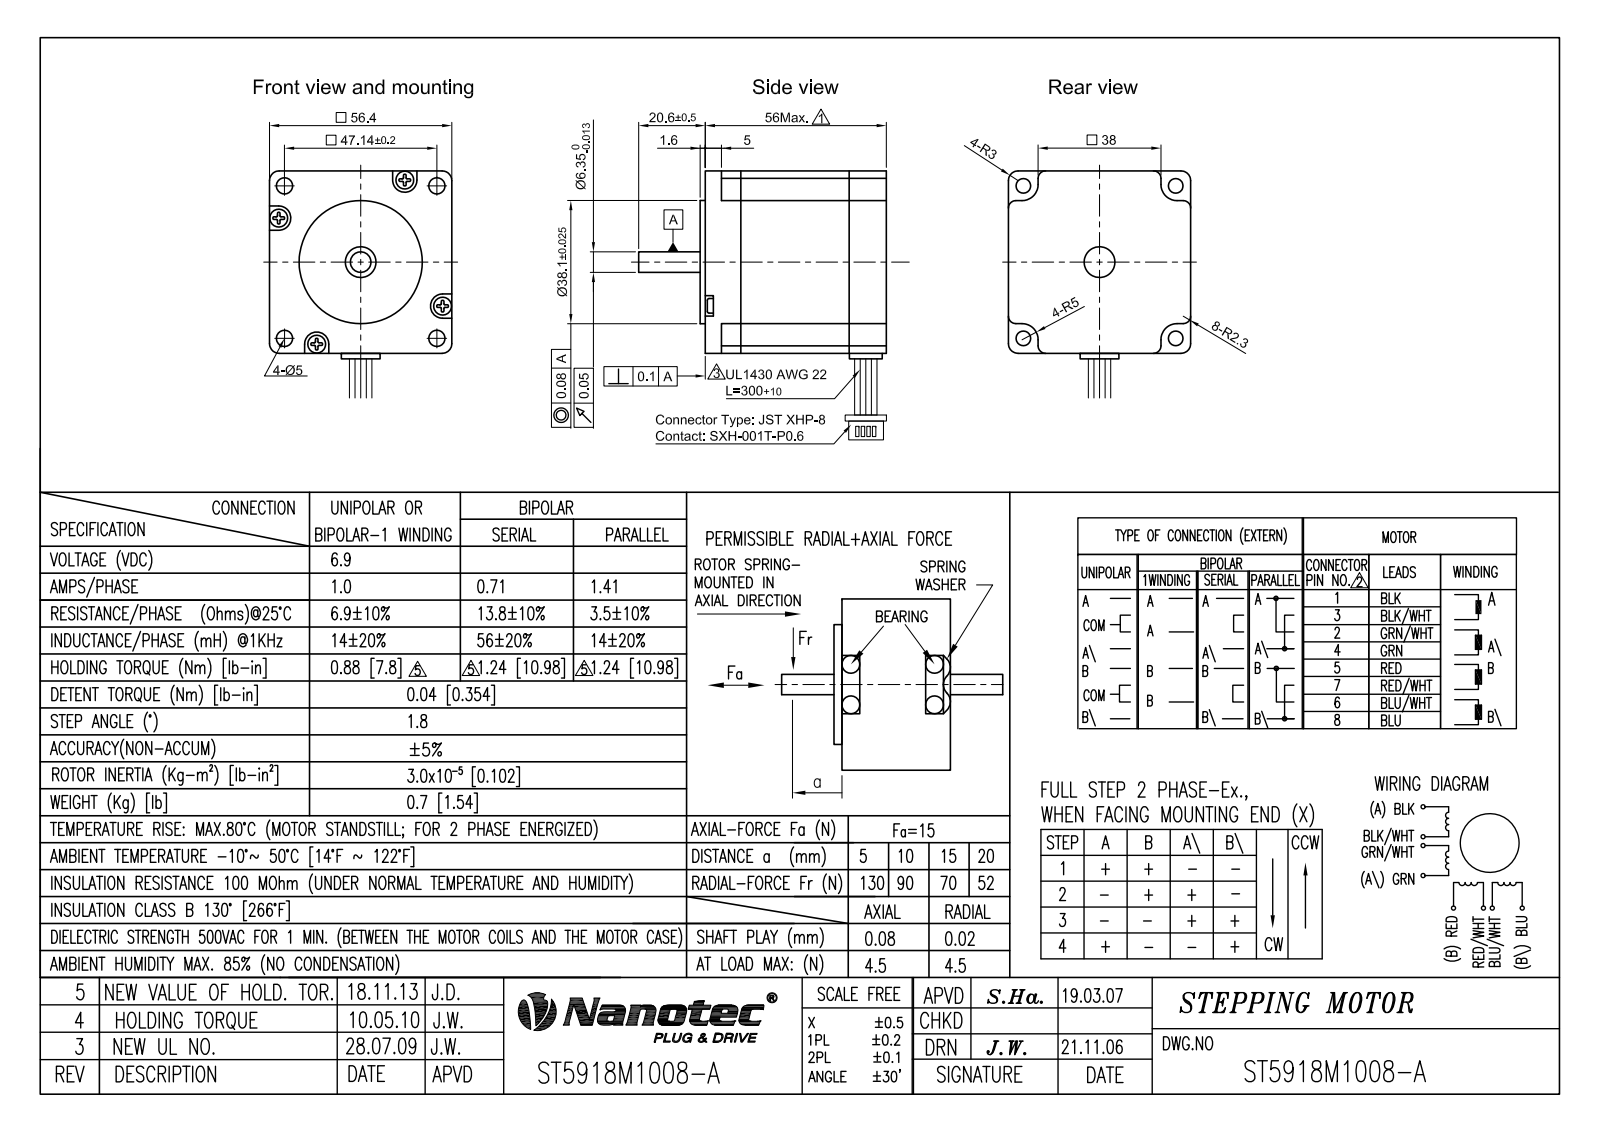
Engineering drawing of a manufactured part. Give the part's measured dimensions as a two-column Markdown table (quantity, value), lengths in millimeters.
| quantity | value |
| --- | --- |
| part name | ST5918M2008-A |
| STEP written by | Autodesk Inventor 2017 (AUTOMOTIVE_DESIGN) |
| units | millimeters |
| bodies | 16 solids, 320 faces (158 planar, 90 cylindrical, 72 other) |
| overall size | 76.6 × 73.37 × 56.94 |
| volume | 162 833 mm³ |
| surface area | 32 356 mm² |
| round holes (diameter × count) | 2.46 × 4, 3.2 × 4, 5 × 4, 1 × 1, 6.35 × 1, 10 × 1 |
| round bosses / shafts (diameter × count) | 1 × 8, 3 × 4, 2.75 × 4, 38.1 × 1 |
| partial cylindrical surfaces (radius × count) | 2.3 × 8, 3 × 4, 3.75 × 4, 5 × 4 |
| main face-to-face distances | 33, 56.4, 12, 45, 56, 44, 11, 57.6, 45.6, 12.6 |
| hole center spacings | 7.95, 30, 39.47, 42.43, 49.64, 62.92, 13.6, 31.7 |
